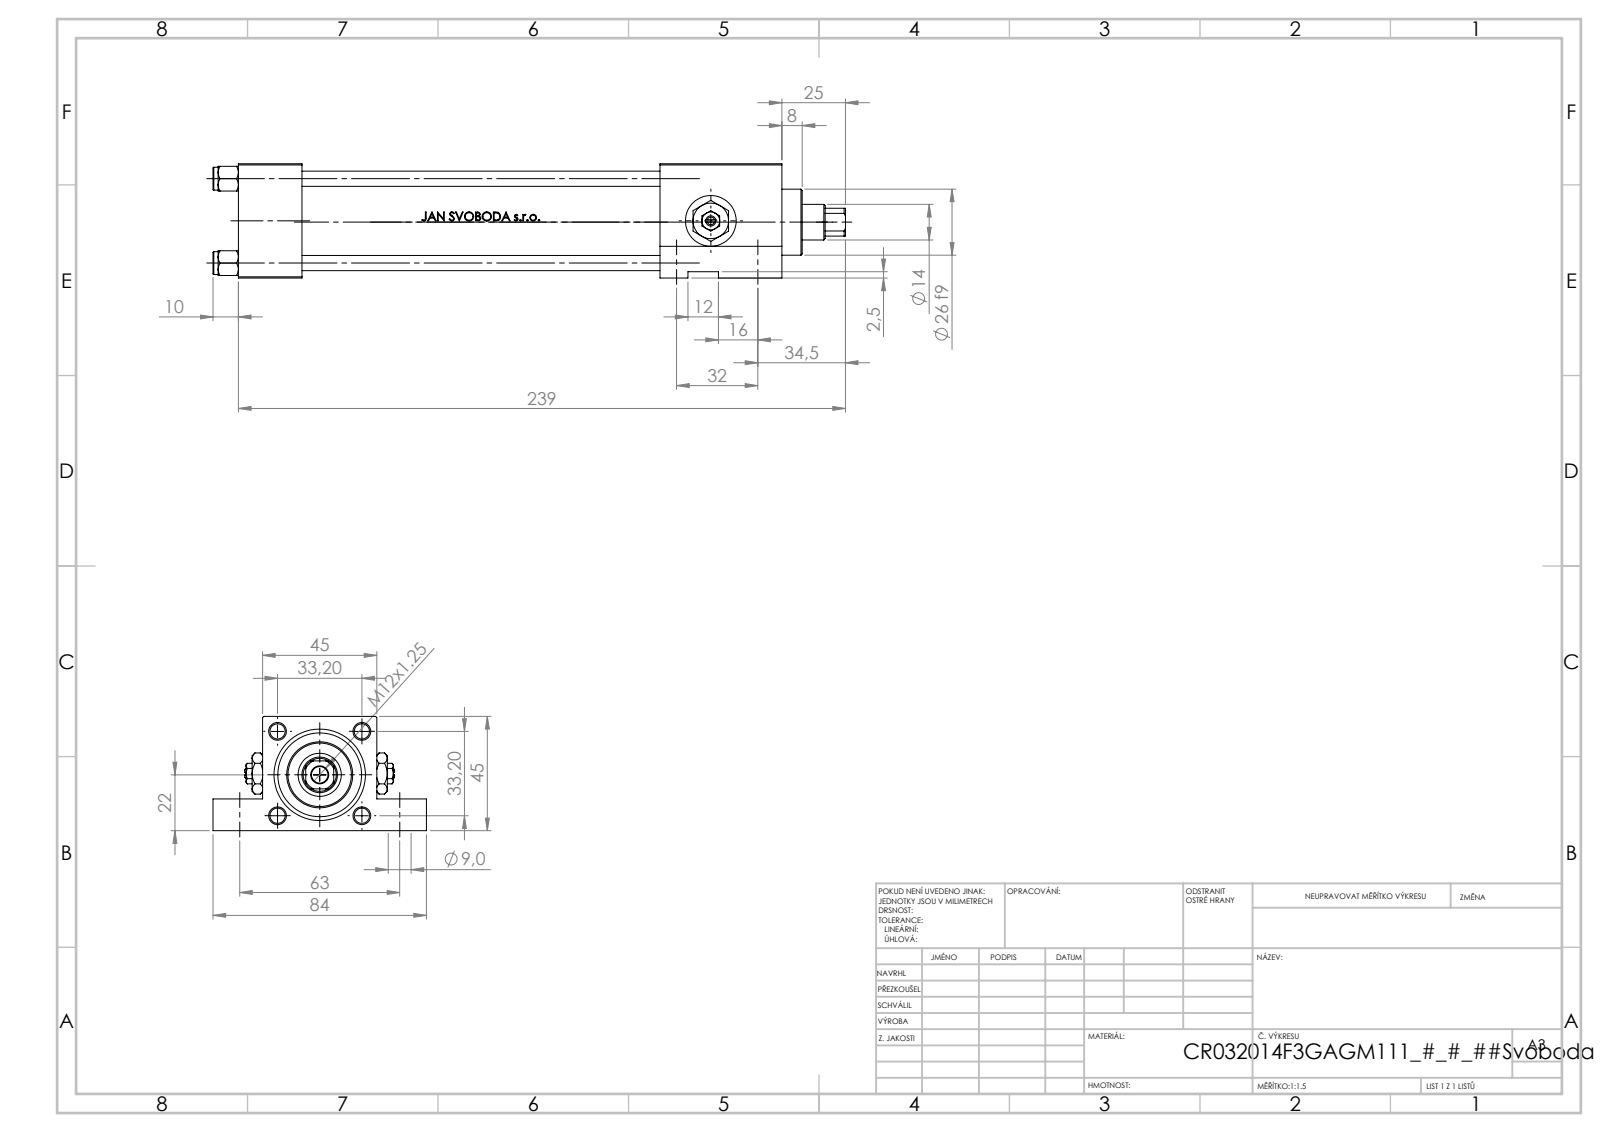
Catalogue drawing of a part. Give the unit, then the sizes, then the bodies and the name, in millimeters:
Units: millimetres
Overall size (bounding box): 249 × 84 × 45
Round holes (diameter × count): ⌀6 ×4, ⌀9 ×4, ⌀7 ×3, ⌀20 ×3, ⌀13.16 ×2, ⌀6.5 ×1, ⌀13 ×1, ⌀14 ×1, ⌀17 ×1, ⌀24 ×1, ⌀32 ×1, ⌀33 ×1
Round bosses / shafts (diameter × count): ⌀9 ×4, ⌀38 ×1, ⌀26 ×1
Partial cylindrical surfaces — rounded edges, fillets, slot ends (radius × count): R6.5 ×1
Main face-to-face distances: 45, 25, 189, 214, 32.5, 166, 141, 48, 12.5, 10
Hole centre spacings: 33.2, 23.13, 23.83, 32, 46.95, 63, 70.66, 163.07
Volume: 266 304 mm³ · Surface area: 105 199 mm²
Bodies: 13 solids, 1195 faces (481 planar, 132 cylindrical, 582 other)
Part name (STEP PRODUCT): V215CR_F_TYCINKA; V215CR_VCP_F; NUT_M5_F; V215CR_F_Body (+2 more)
STEP written by: SolidWorks 2019 (CONFIG_CONTROL_DESIGN)
